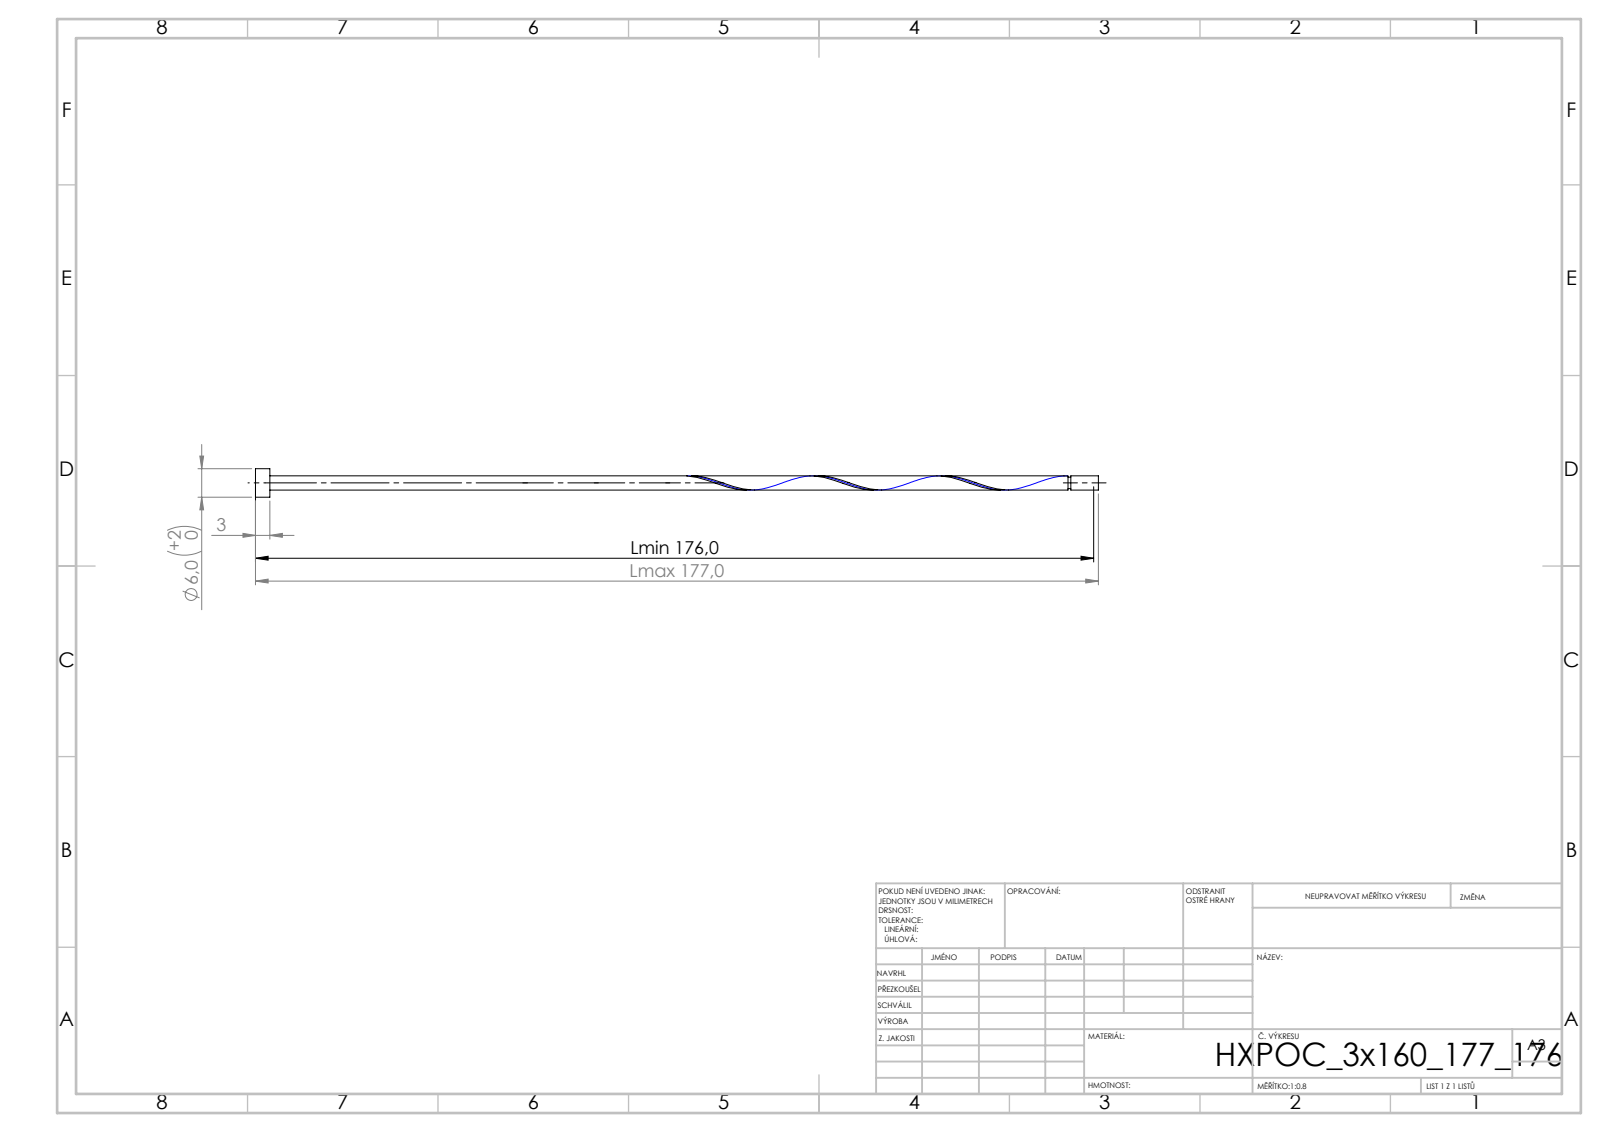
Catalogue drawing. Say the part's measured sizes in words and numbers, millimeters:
Its 3-D file was written by "SolidWorks 2019 (CONFIG_CONTROL_DESIGN)". It is 1 solid with 16 faces: 6 planar, 9 cylindrical and 1 other. Overall it measures 177 by 6 by 6 millimeters. Its volume is 1 554 cubic millimeters and its surface area 2 284 square millimeters. Round bosses or shafts: 1 of diameter 6, 1 of diameter 3, 1 of diameter 2.4. The main face-to-face distances are 3, 177, 174, 171.22, 168.22, 5.78, 170.62, 167.62, 0.6, 6.38.
